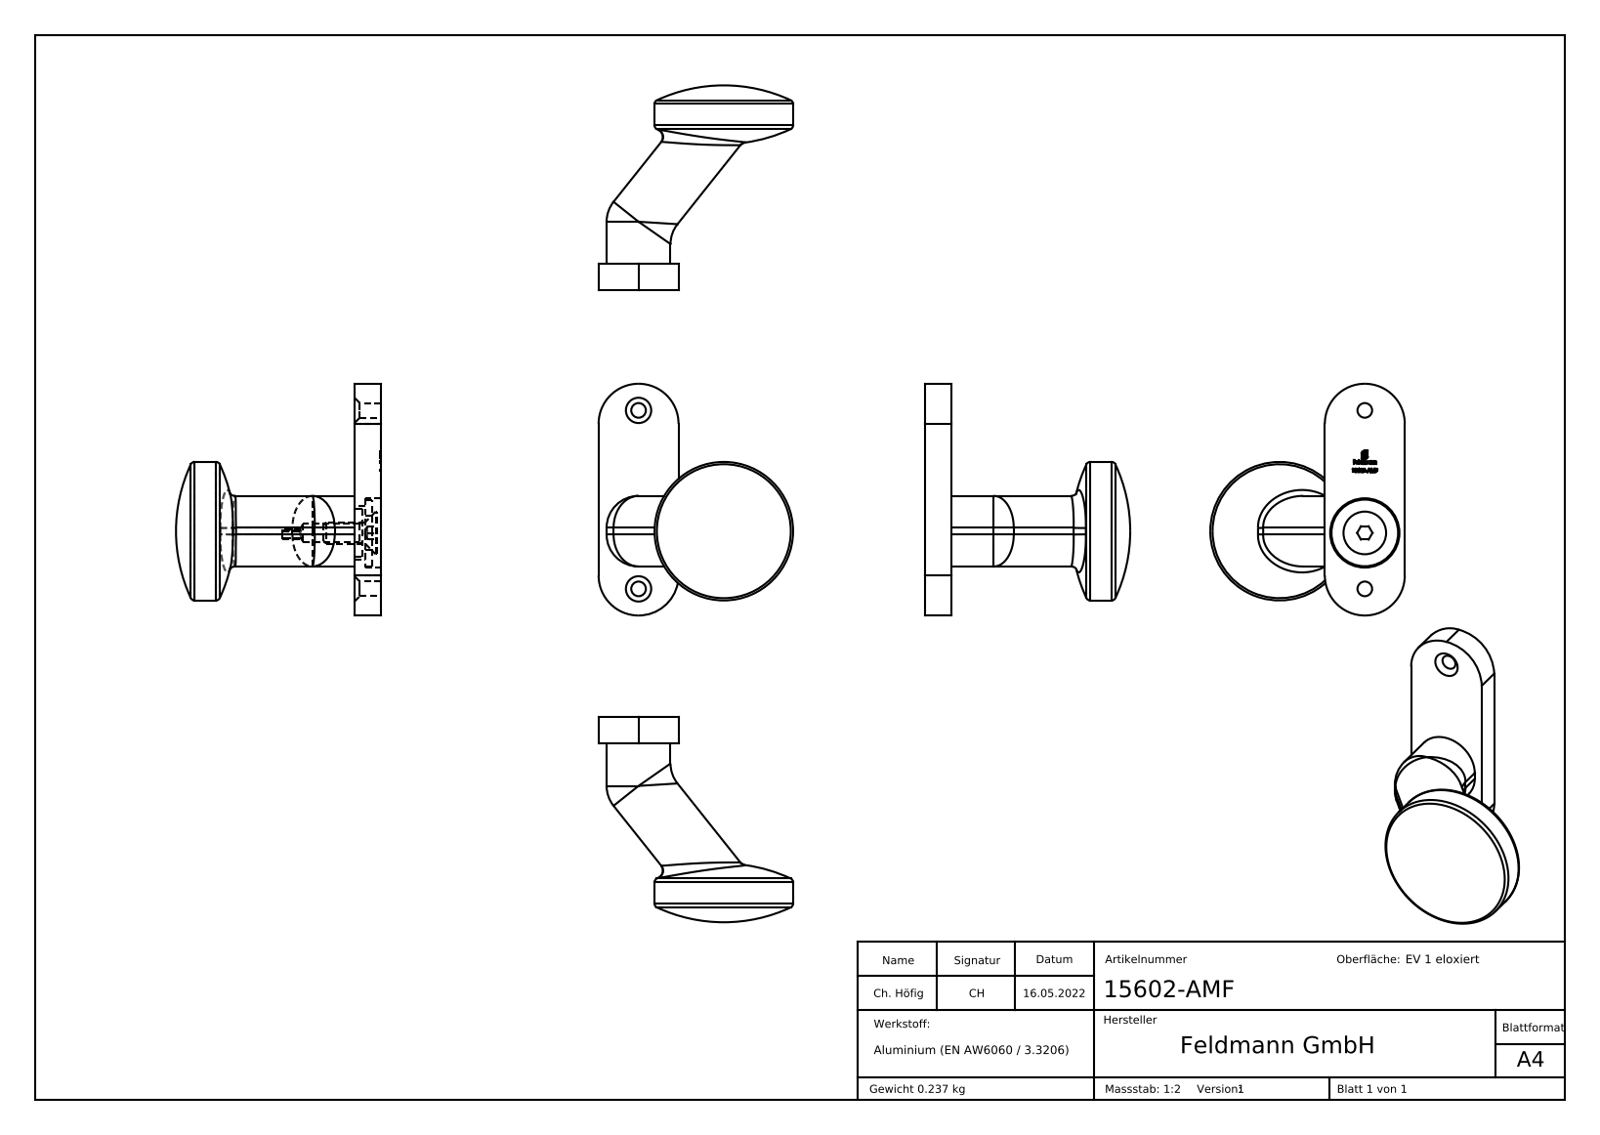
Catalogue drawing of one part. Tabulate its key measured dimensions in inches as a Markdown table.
| quantity | value |
| --- | --- |
| part name | 15602-AMF Teil3_15602-AMF Teil3; 15602-AMF; DIN 7991 Konfig_M8x20; 15602-AMF Teil2_15602-AMF Teil2 (+1 more) |
| STEP written by | SolidWorks 2018 (CONFIG_CONTROL_DESIGN) |
| units | inches |
| bodies | 4 solids, 329 faces (185 planar, 25 cylindrical, 119 other) |
| overall size | 3.425 × 3.031 × 2.874 |
| volume | 5.096 in³ |
| surface area | 31.5 in² |
| round holes (diameter × count) | 0.217 × 2, 0.268 × 1, 0.512 × 1, 0.787 × 1, 1.024 × 1 |
| round bosses / shafts (diameter × count) | 2.047 × 1, 0.984 × 1, 0.701 × 1, 0.63 × 1, 0.315 × 1 |
| partial cylindrical surfaces (radius × count) | 0.472 × 6, 0.01 × 4, 0.591 × 2 |
| main face-to-face distances | 0.394, 1.181, 0.236, 0.157, 0.138, 0.256, 0.098, 0.118, 0.063, 0.276 |
| hole center spacings | 0.827, 1.811, 2.638 |
